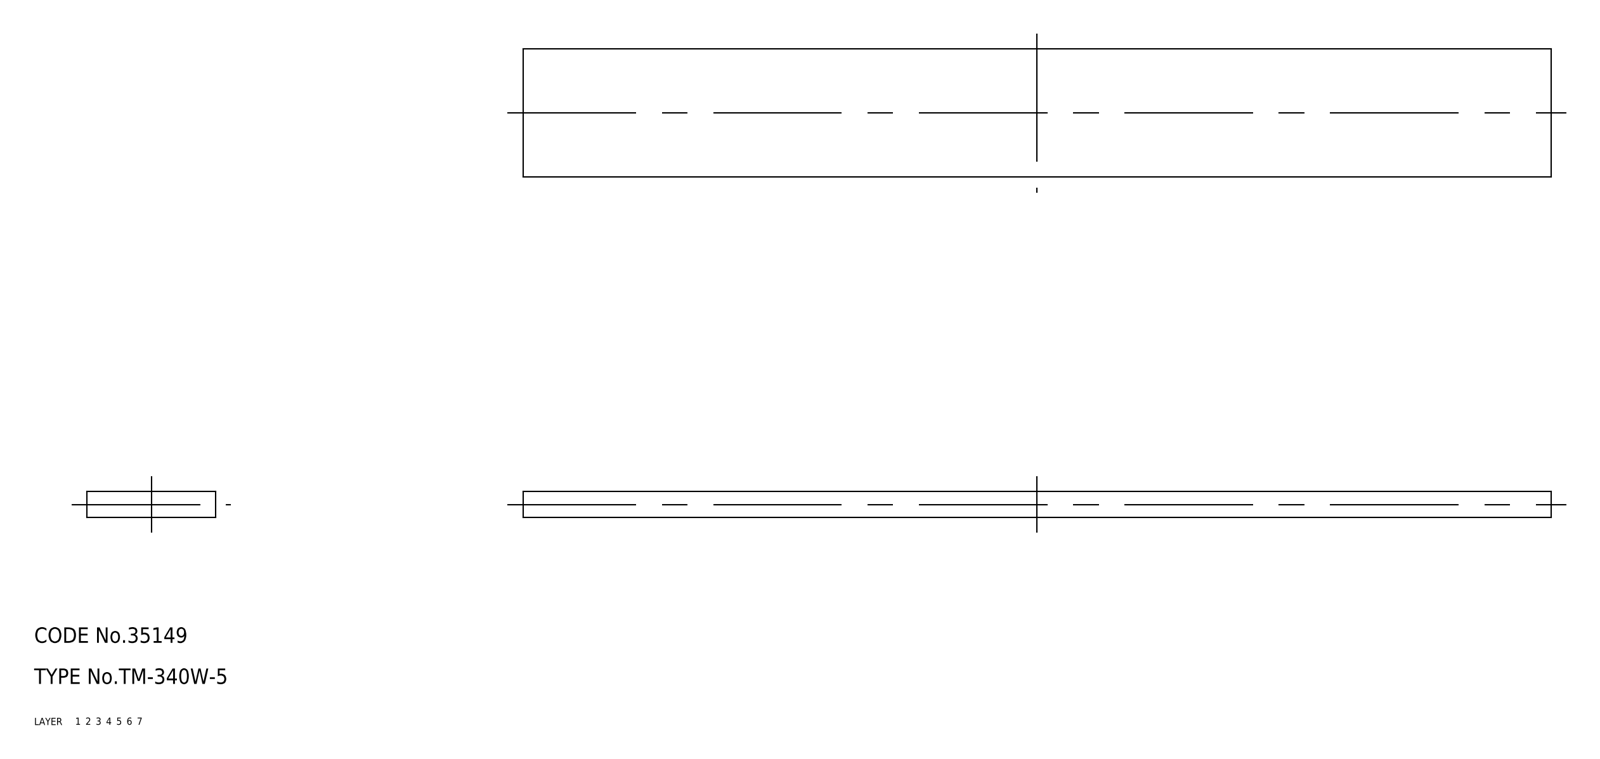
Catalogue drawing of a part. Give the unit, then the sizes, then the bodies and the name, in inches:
Units: inches
Overall size (bounding box): 7.874 × 0.984 × 0.197
Main face-to-face distances: 0.197, 0.984, 7.874
Volume: 1.526 in³ · Surface area: 18.99 in²
Bodies: 1 solid, 6 faces (6 planar, 0 cylindrical, 0 other)
Part name (STEP PRODUCT): TM_340W_5; rubber foam
STEP written by: SolidWorks 2015 (AUTOMOTIVE_DESIGN)
